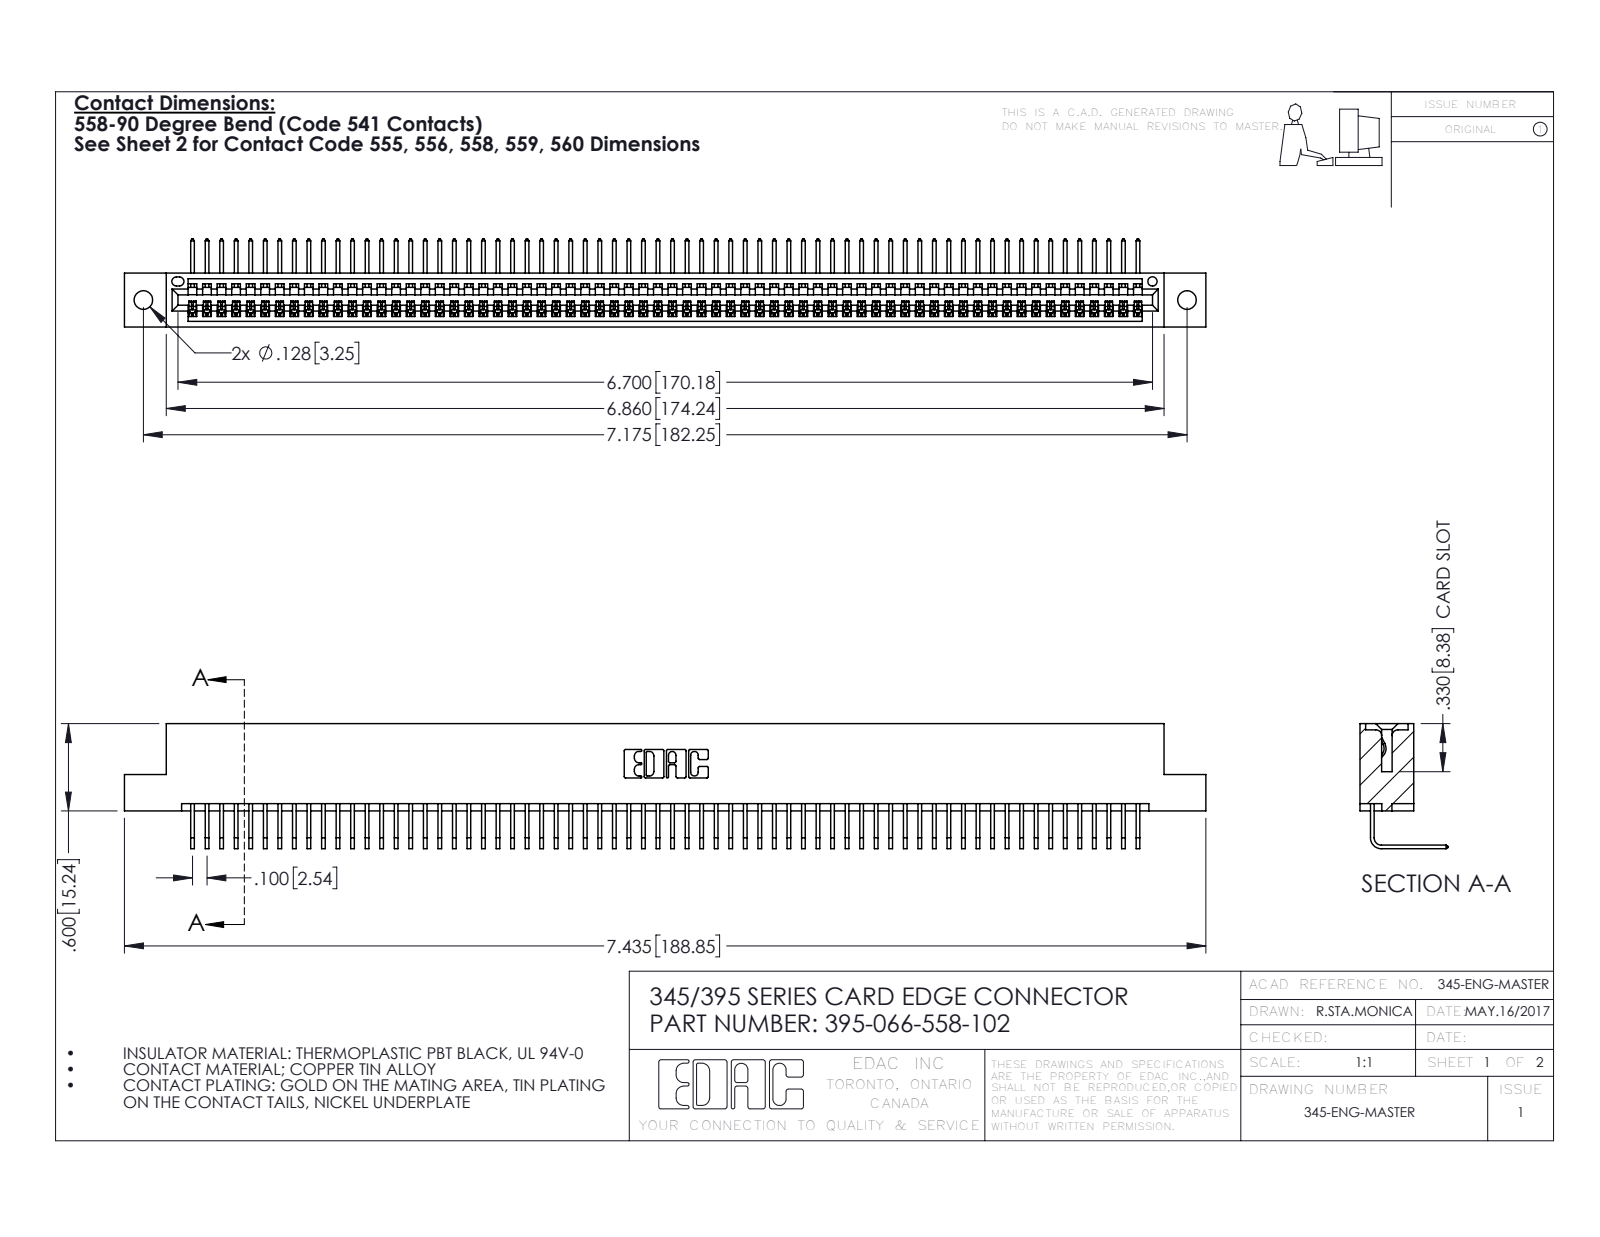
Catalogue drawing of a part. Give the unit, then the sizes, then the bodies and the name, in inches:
Units: inches
Overall size (bounding box): 7.435 × 0.859 × 0.605
Round holes (diameter × count): ⌀0.128 ×2, ⌀0.064 ×1
Partial cylindrical surfaces — rounded edges, fillets, slot ends (radius × count): R0.006 ×132, R0.01 ×22, R0.007 ×6, R0.031 ×6, R0.026 ×3, R0.031 ×2, R0.04 ×2, R0.014 ×1
Main face-to-face distances: 0.298, 0.072, 0.37, 0.2, 0.098, 0.272, 0.025, 0.225, 0.149, 0.072
Hole centre spacings: 0.27, 6.939, 7.175
Volume: 1.118 in³ · Surface area: 39.82 in²
Bodies: 67 solids, 4086 faces (2852 planar, 1234 cylindrical, 0 other)
Part name (STEP PRODUCT): 345 Part_Flush Mounting Lugs - 0.128 Dia; 345-292-001_558 Tail - 2; 395-066-558-102
STEP written by: SolidWorks 2016 (CONFIG_CONTROL_DESIGN)
